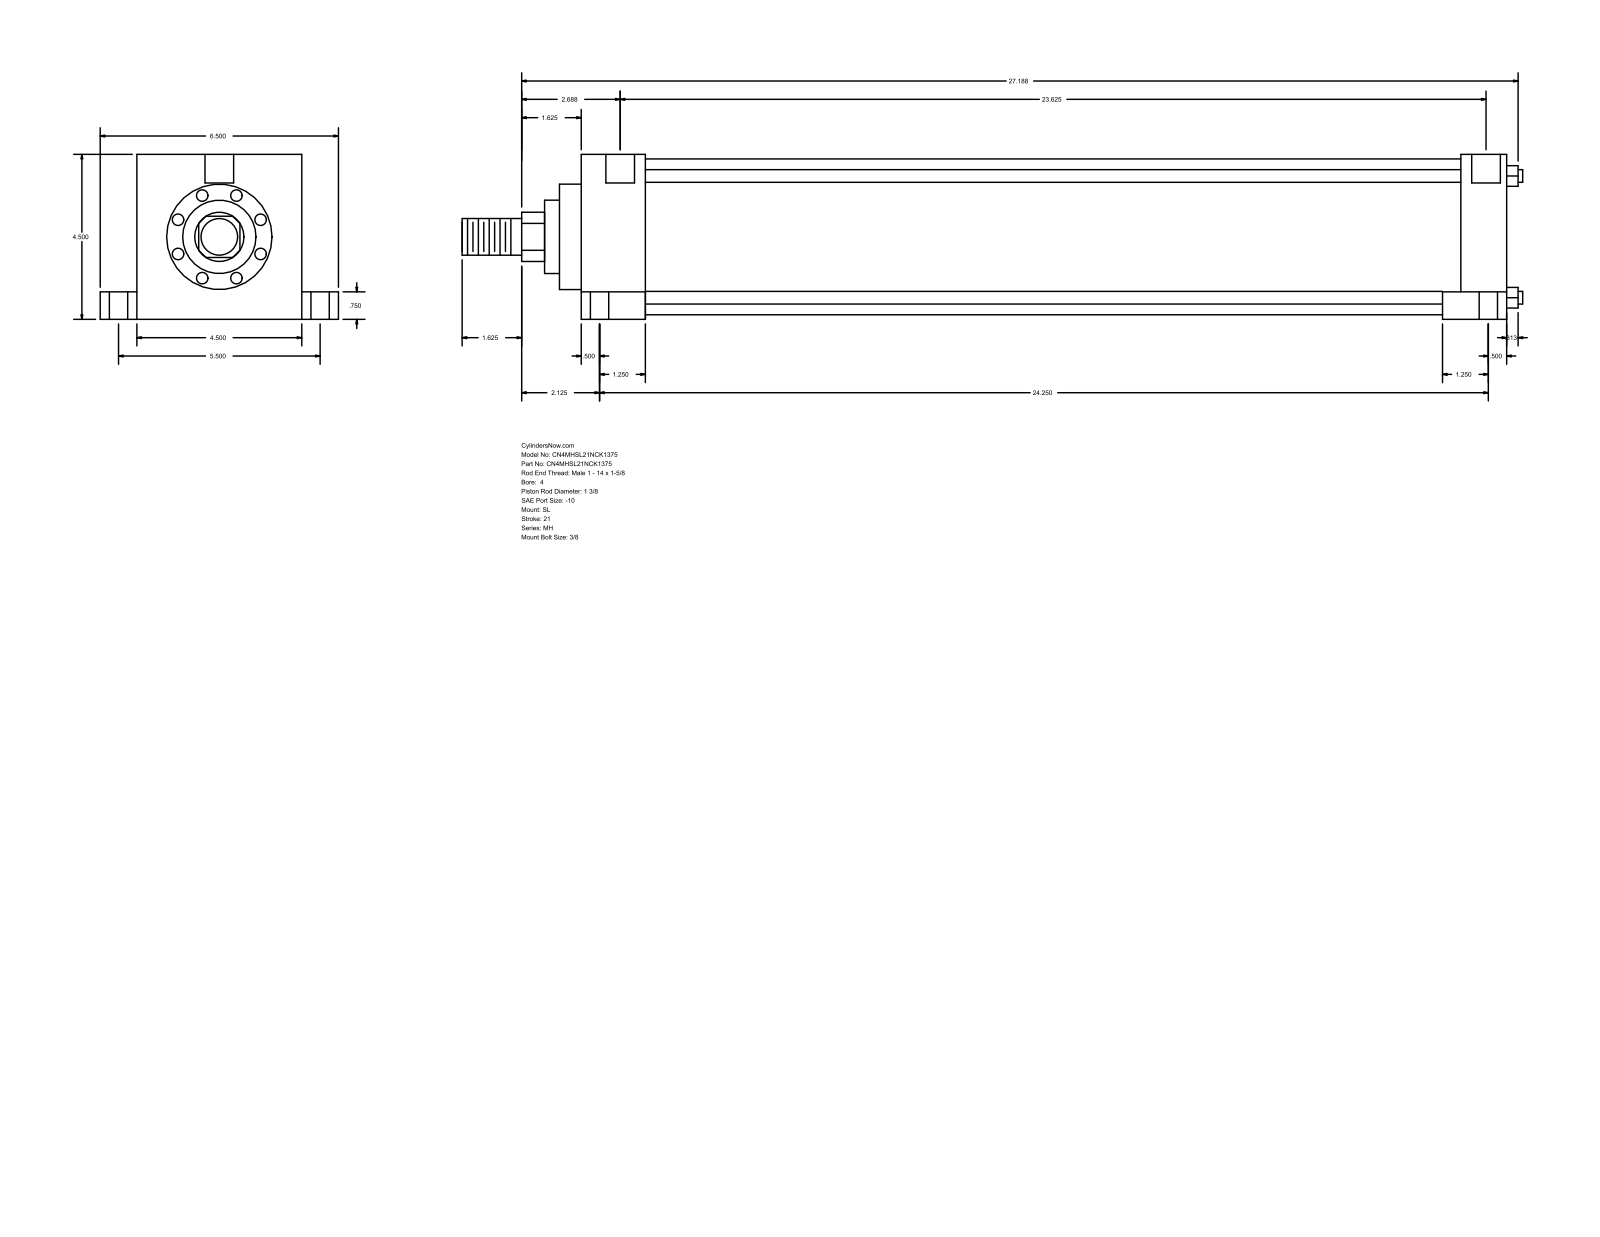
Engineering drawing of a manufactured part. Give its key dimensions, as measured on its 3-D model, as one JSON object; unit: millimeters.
{"part_name": "MH_SL__0400_1.375", "step_written_by": "GSSL Pune (CONFIG_CONTROL_DESIGN)", "units": "millimeters", "bodies": {"solids": 0, "faces": 110, "planar": 77, "cylindrical": 33, "other": 0}, "overall_size": [735.01, 165.1, 114.3], "round_holes": [[8.73, 4], [12.7, 4], [19.05, 4], [19.84, 2]], "round_bosses_or_shafts": [[8.76, 4], [107.95, 1], [73.03, 1], [50.8, 1], [34.92, 1], [25.4, 1]], "partial_cylinders_radius": [[17.06, 1]], "face_to_face_distances": [114.3, 641.35, 44.45, 596.9, 609.61, 565.16, 31.74, 25.4, 139.7, 19.05], "hole_center_spacings": [69.85, 69.87, 70.99, 71.29, 139.7, 603.25, 605.7, 607.28]}
